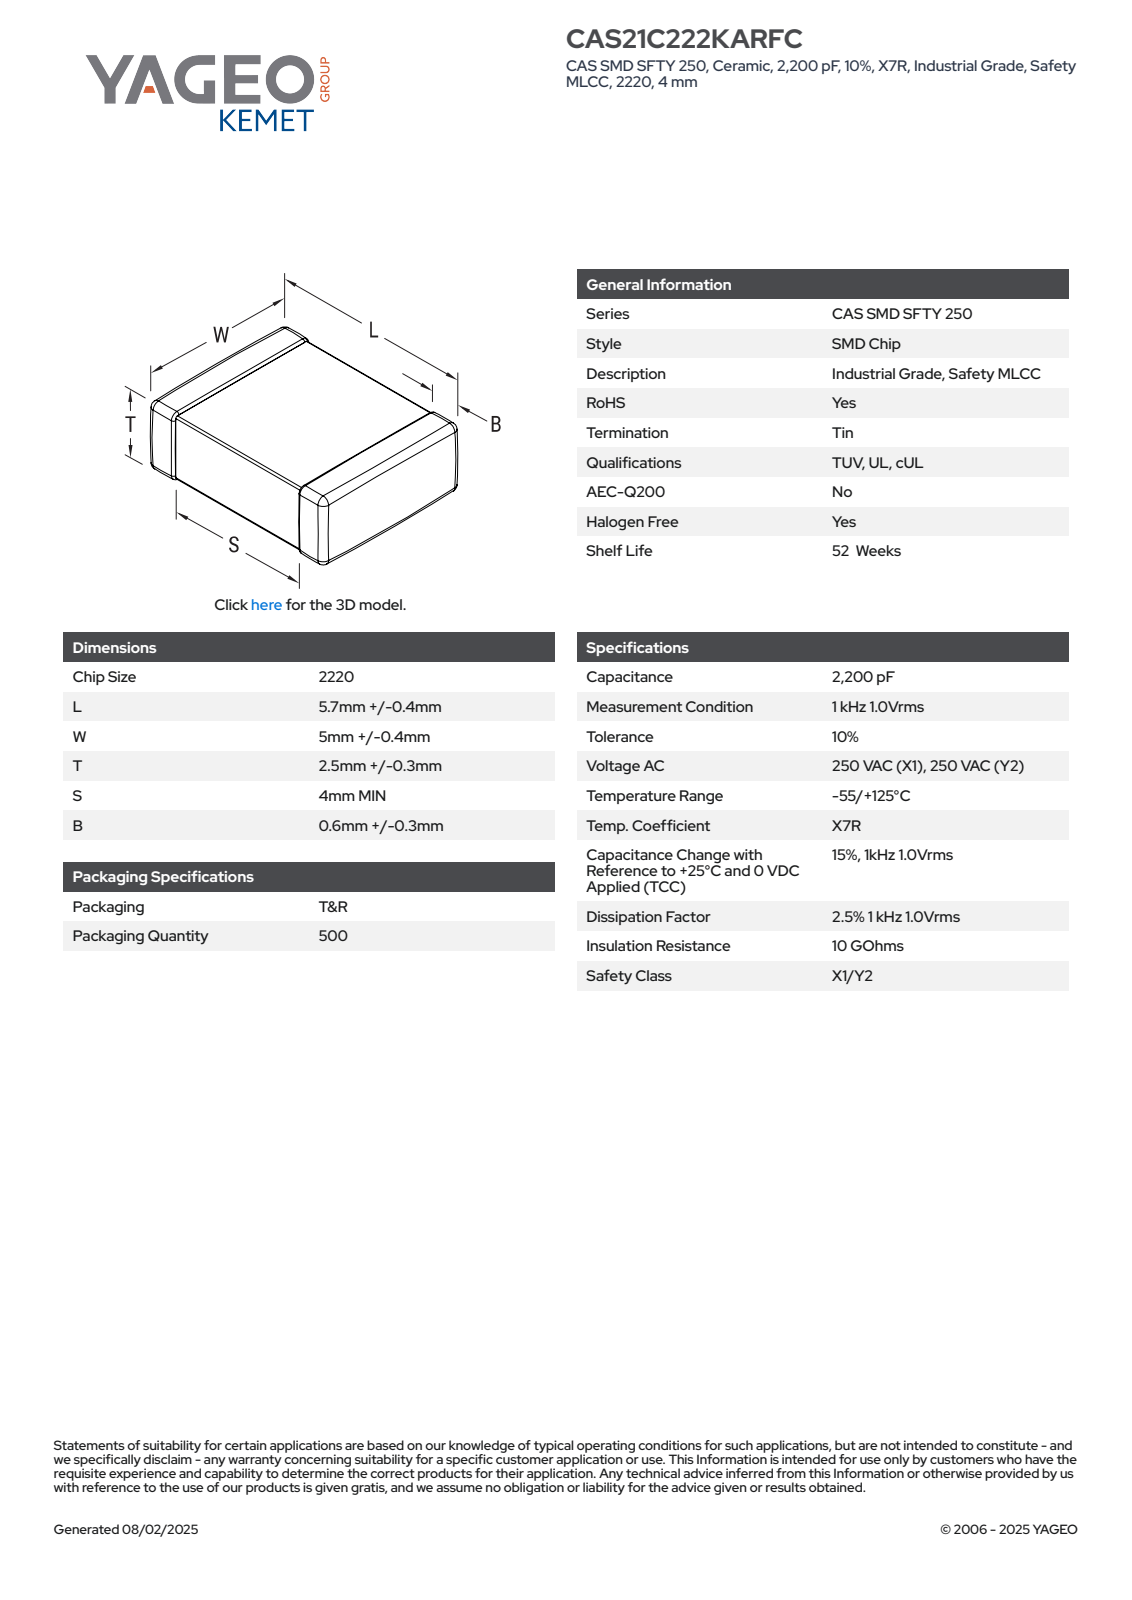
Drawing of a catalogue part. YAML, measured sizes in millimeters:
part_name: "CCS_CCSTD_2220_L6.1W5.4T2.8B0.6"
step_written_by: "SolidWorks 2021 (AUTOMOTIVE_DESIGN)"
units: millimeters
bodies: {solids: 4, faces: 121, planar: 71, cylindrical: 34, other: 16}
overall_size: [6.1, 5.4, 2.8]
volume: 84
surface_area: 130
partial_cylinders:
  - {radius: 0.11, count: 24}
face_to_face_distances: [2.58, 2.69, 6.1, 5.18, 2.8, 5.29, 5.4, 2.5, 3.6, 3.29]
